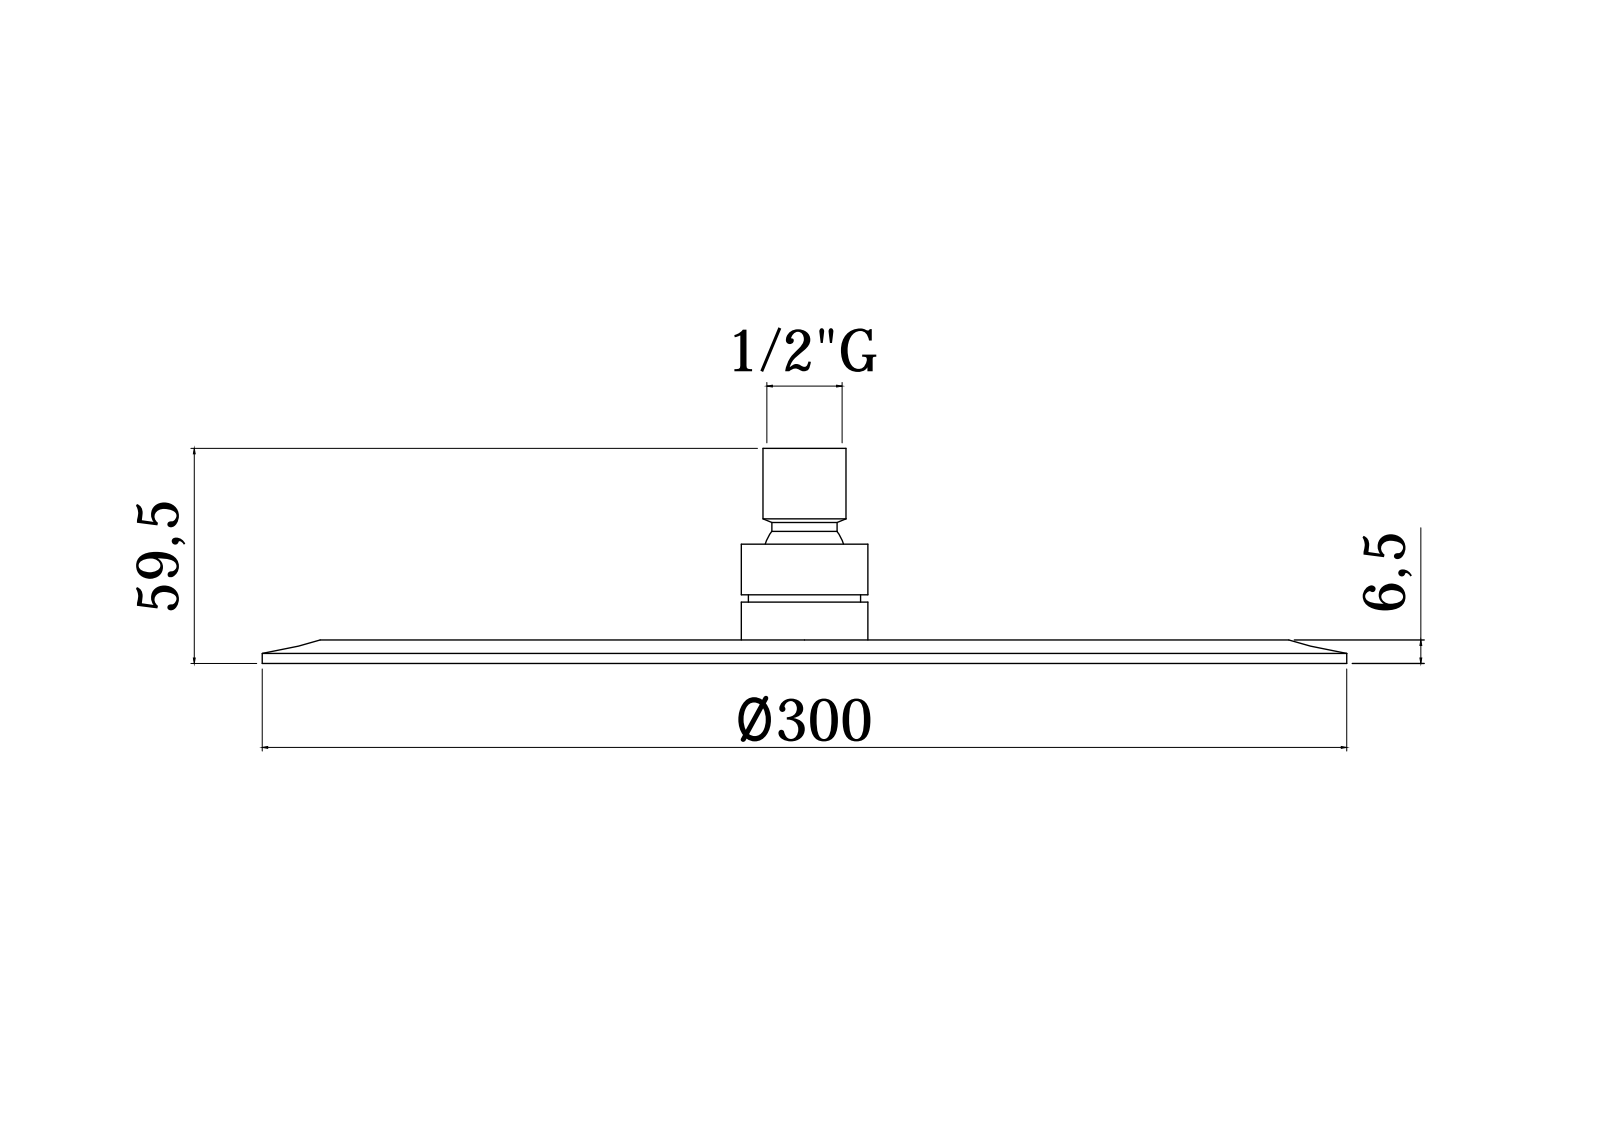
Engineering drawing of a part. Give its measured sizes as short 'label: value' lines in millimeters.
name: 4072055CRX-B_SCOCCA_1; 4072055CRX-B_SCOCCA_2; 4072055CRX-B_UGELLI_1; 4072055CRX-B_UGELLI_2 (+8 more)
written by: CREO PARAMETRIC BY PTC INC, 2020044 (CONFIG_CONTROL_DESIGN)
unit: mm
bodies: 10 solids, 3071 faces (493 planar, 788 cylindrical, 1790 other)
size: 300 × 300 × 56.5
volume: 183 063 mm³; area: 419 364 mm²
holes: 80× ⌀4, 1× ⌀2.28, 1× ⌀3.4, 1× ⌀5, 1× ⌀12, 1× ⌀14, 1× ⌀14.1, 1× ⌀15.2, 1× ⌀15.5, 1× ⌀19, 1× ⌀21, 1× ⌀21.3
bosses: 80× ⌀5.5, 80× ⌀3.9, 80× ⌀2.5, 1× ⌀300, 1× ⌀254, 1× ⌀36, 1× ⌀30, 1× ⌀27.1
rounds: 1× R7.51, 1× R9.1, 1× R11.75, 1× R13.15, 1× R14.25
face distances: 1, 5, 4, 6, 4.6, 1.4, 0.4, 3.6, 2, 3
hole spacings: 134.37, 96.88, 126.58, 50.26, 81.32, 26.72, 26.73, 52.43
